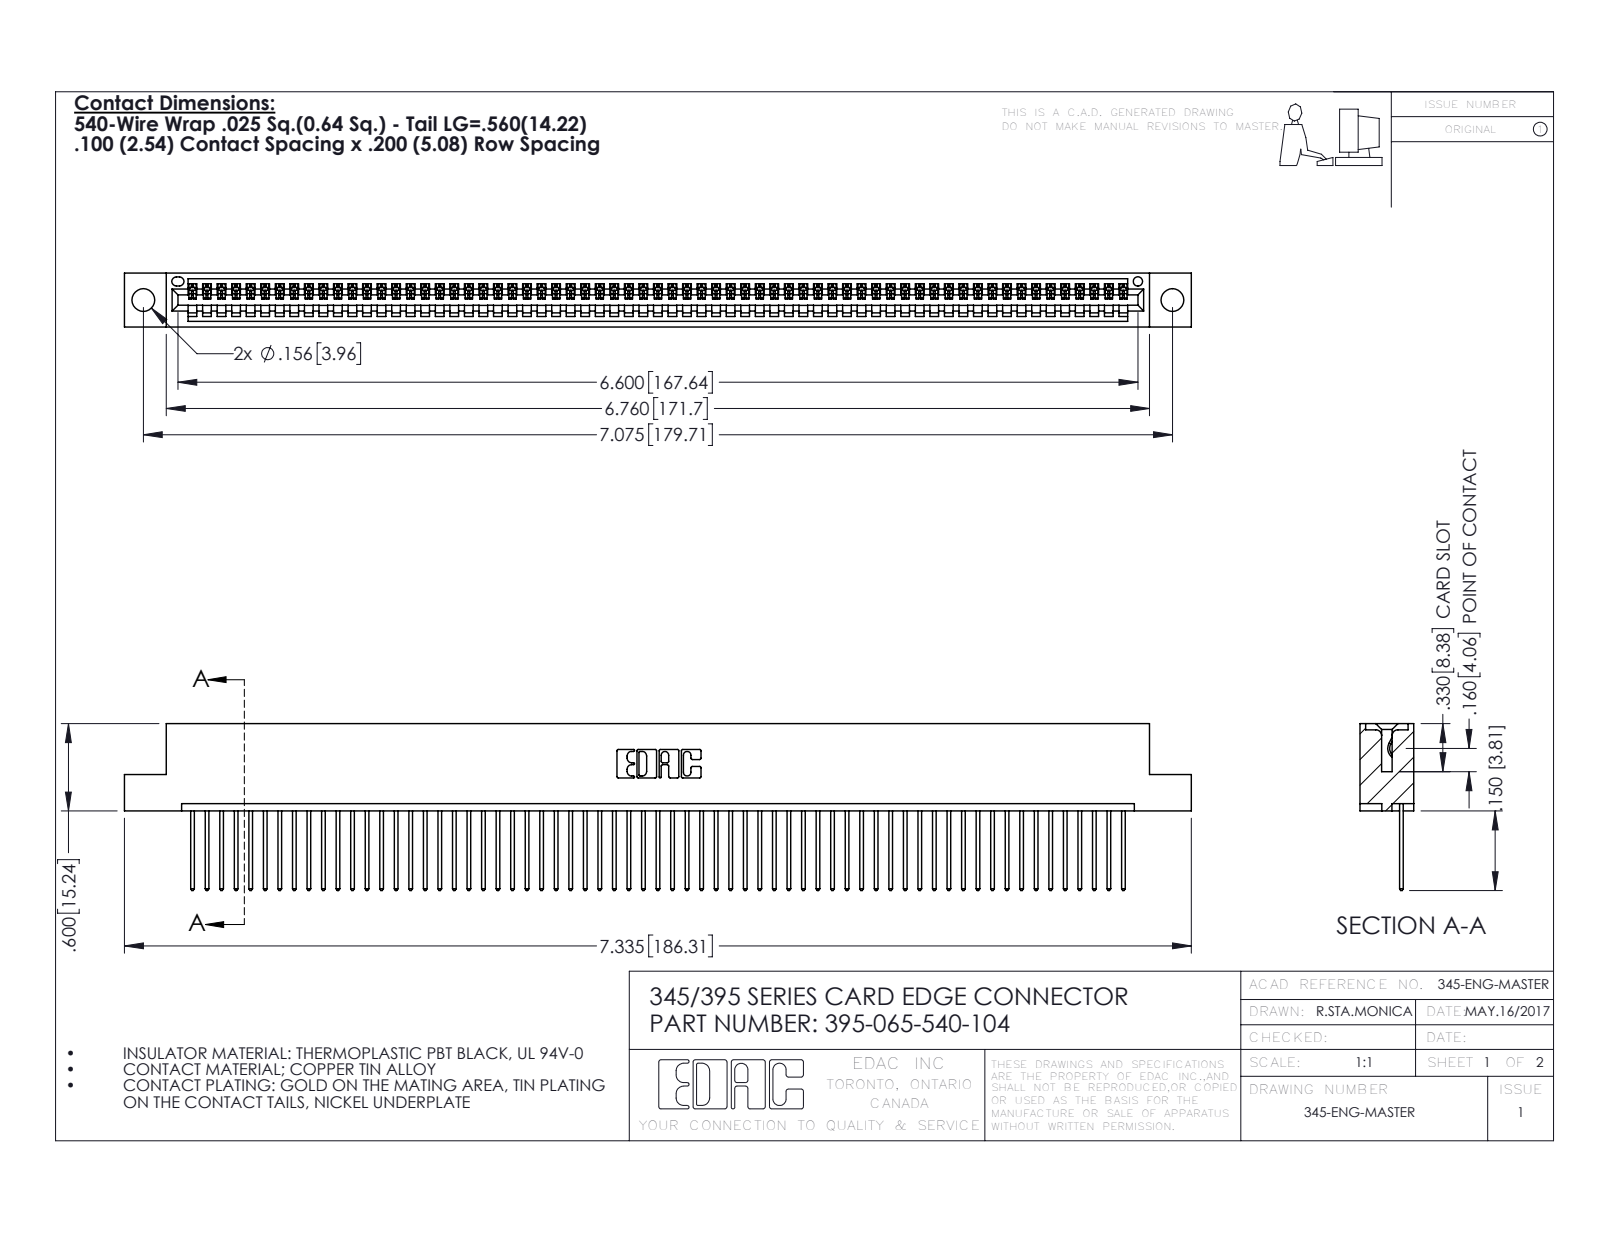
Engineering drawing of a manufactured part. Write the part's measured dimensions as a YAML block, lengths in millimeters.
part_name: "395-065-540-104; 345 Part_Flush Mounting Lugs - 0.156 Dia-TH; 345-292-001_345-293-140"
step_written_by: "SolidWorks 2016 (CONFIG_CONTROL_DESIGN)"
units: millimeters
bodies: {solids: 66, faces: 3896, planar: 2680, cylindrical: 1216, other: 0}
overall_size: [186.3, 29.1, 9.4]
volume: 17880
surface_area: 24520
round_holes:
  - {diameter: 4, count: 2}
  - {diameter: 1.6, count: 1}
partial_cylinders:
  - {radius: 0.2, count: 130}
  - {radius: 0.3, count: 130}
  - {radius: 0.3, count: 22}
  - {radius: 0.2, count: 6}
  - {radius: 0.8, count: 6}
  - {radius: 0.7, count: 3}
  - {radius: 0.8, count: 2}
  - {radius: 1, count: 2}
face_to_face_distances: [7.6, 1.8, 9.4, 2.5, 6.9, 0.6, 5.1, 5.7, 3.8, 1.8]
hole_center_spacings: [6.9, 173.7, 179.7]
